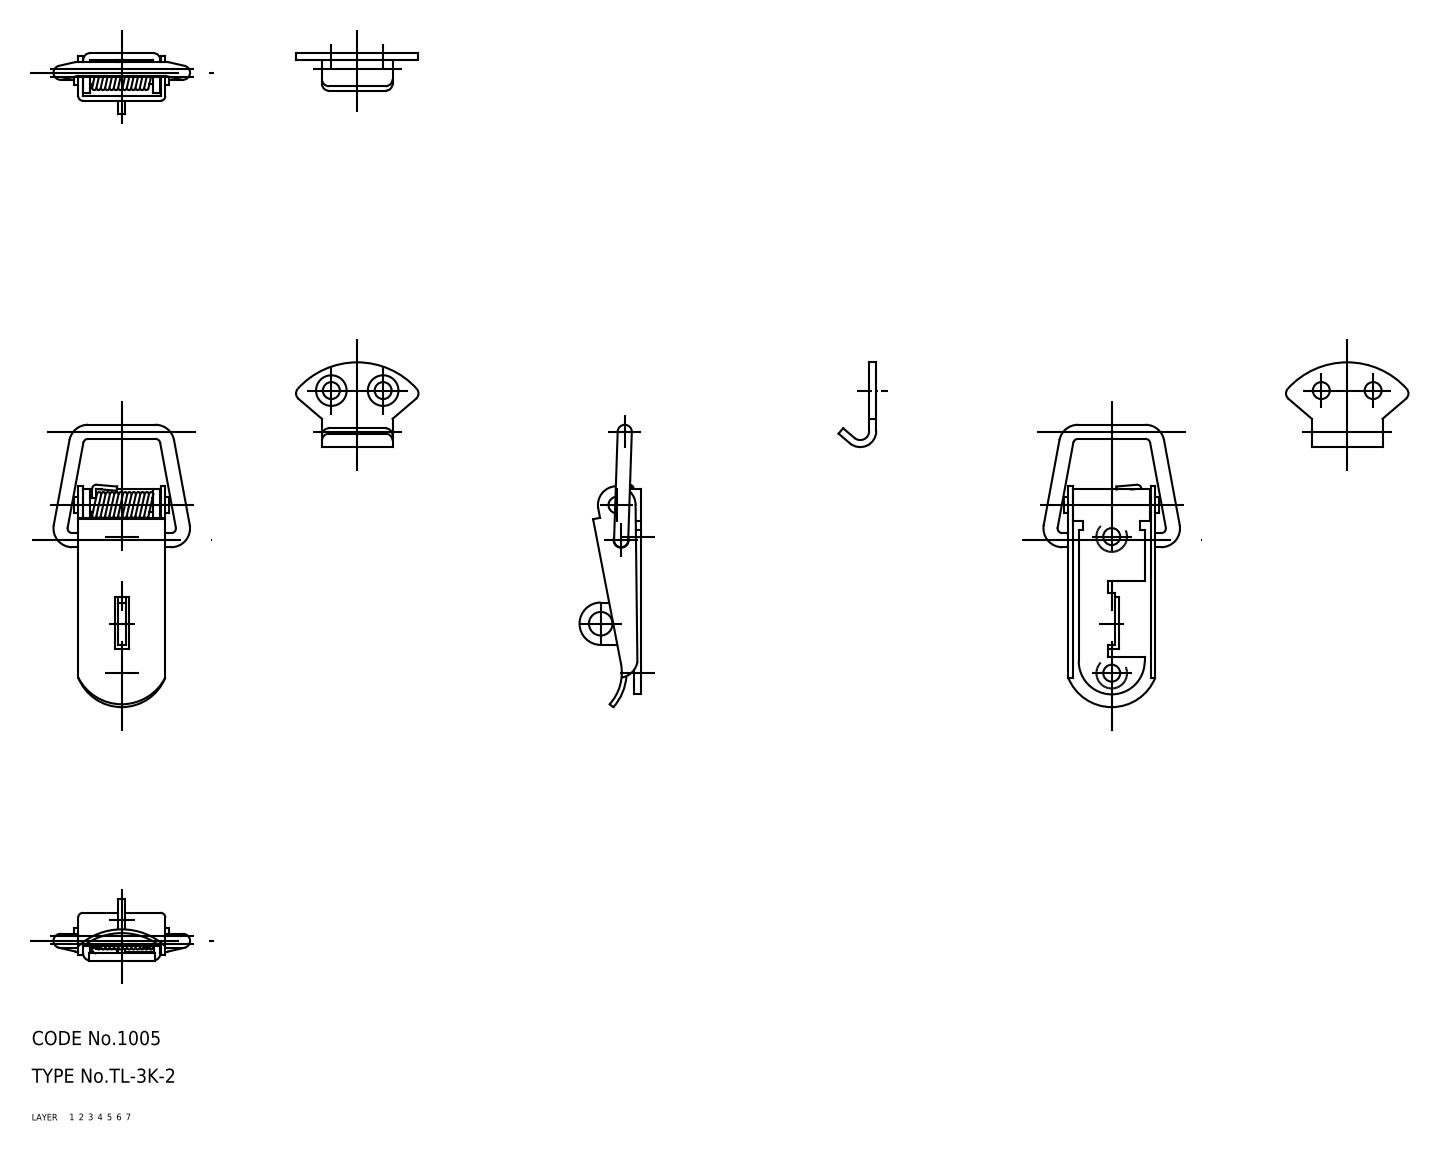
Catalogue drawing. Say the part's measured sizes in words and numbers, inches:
The part is named "67122085; 67122098; 67122111; 67122124 (+2 more)". Its 3-D file was written by "CADfix (AUTOMOTIVE_DESIGN)". It is 7 solids with 168 faces: 0 planar, 0 cylindrical and 168 other. Overall it measures 2.882 by 1.142 by 0.512 inches. Its volume is 0.202 cubic inches and its surface area 9.76 square inches.
